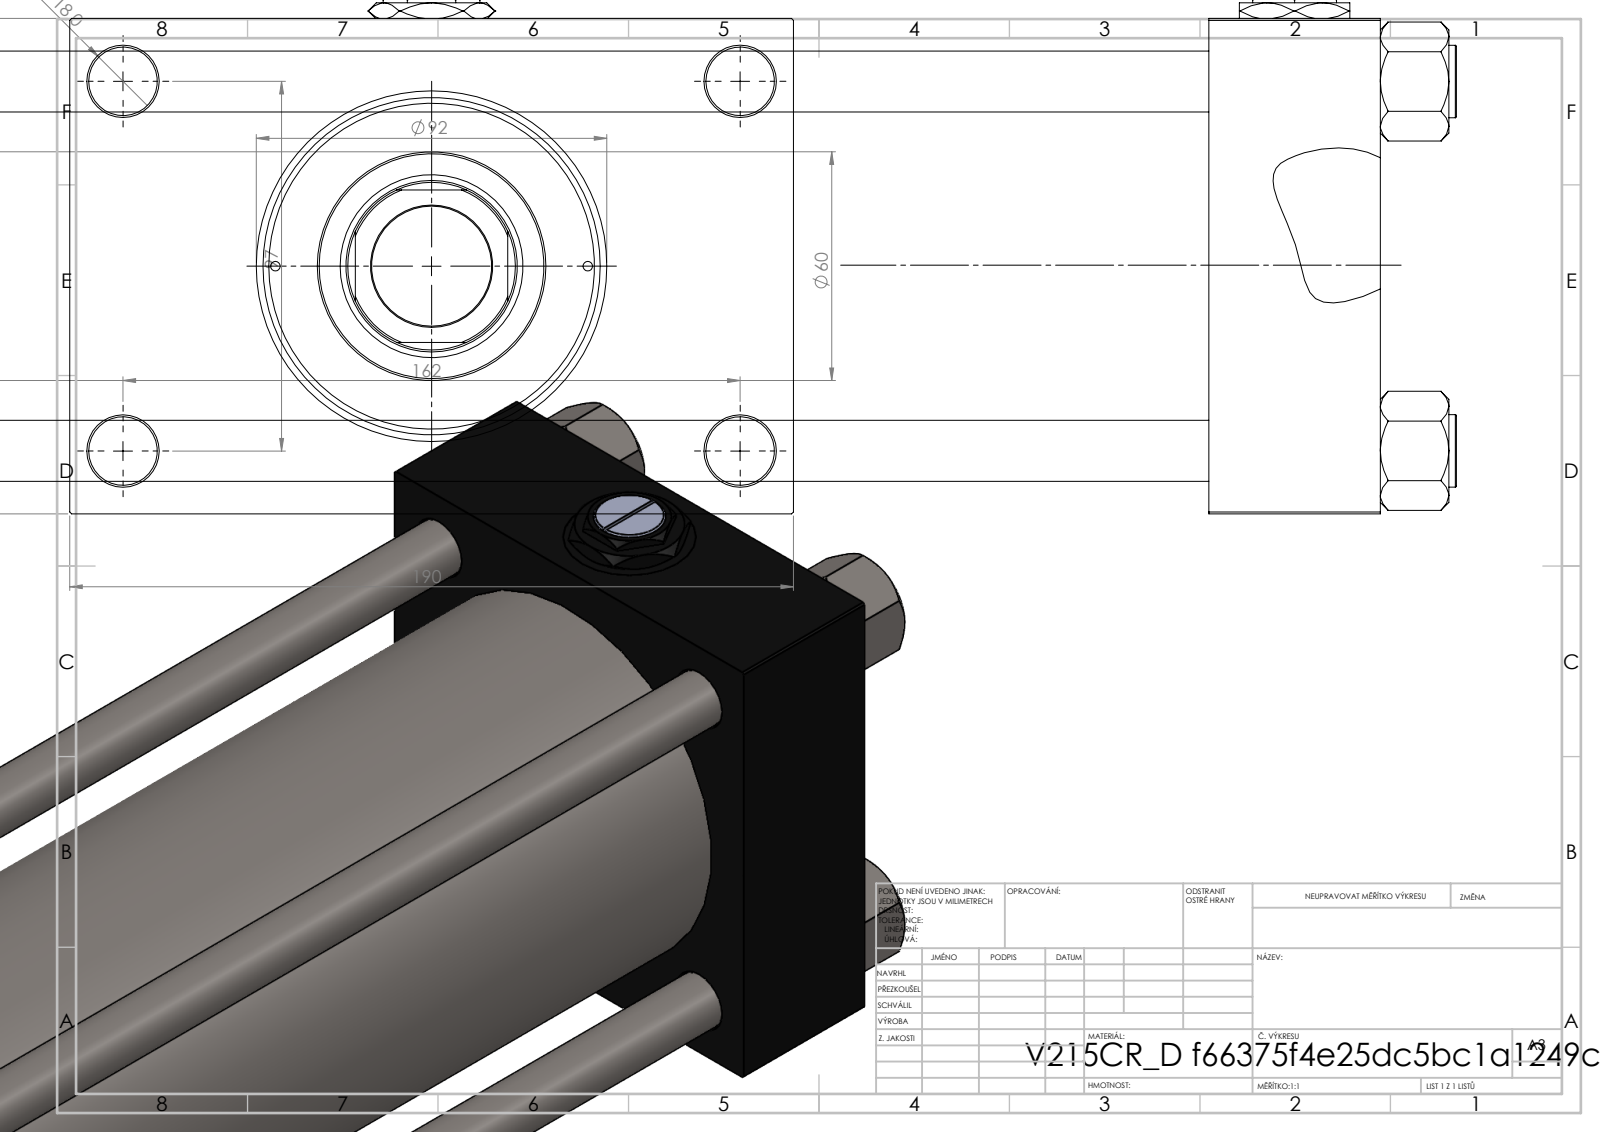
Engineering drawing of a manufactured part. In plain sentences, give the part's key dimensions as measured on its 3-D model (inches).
The part is named "Zatka_pro_OIL_PORT; V215CR_D_Body; V215CR_VCP_D; V215CR_D_TYCINKA (+2 more)". Its 3-D file was written by "SolidWorks 2019 (CONFIG_CONTROL_DESIGN)". It is 13 solids with 1260 faces: 595 planar, 103 cylindrical and 562 other. Overall it measures 20.591 by 7.48 by 5.394 inches. Its volume is 214.7 cubic inches and its surface area 990 square inches. Round holes: 4 of diameter 0.63, 4 of diameter 0.709, 4 of diameter 1.041, 4 of diameter 1.378, 3 of diameter 0.276, 2 of diameter 0.098, 1 of diameter 1.24, 1 of diameter 1.772, 1 of diameter 1.89, 1 of diameter 2.992, 1 of diameter 3.366, 1 of diameter 3.937. Round bosses or shafts: 4 of diameter 0.748, 1 of diameter 4.173, 1 of diameter 3.622, 1 of diameter 2.362. Partial cylindrical surfaces (rounded edges, fillets, slot ends): 1 of radius 0.866. The main face-to-face distances are 1.772, 5.118, 15.591, 13.819, 17.559, 15.787, 1.969, 1.181, 6.299, 3.78. The hole center spacings are 1.281, 1.93, 2.475, 2.698, 3.717, 3.815, 4.005, 4.026.
